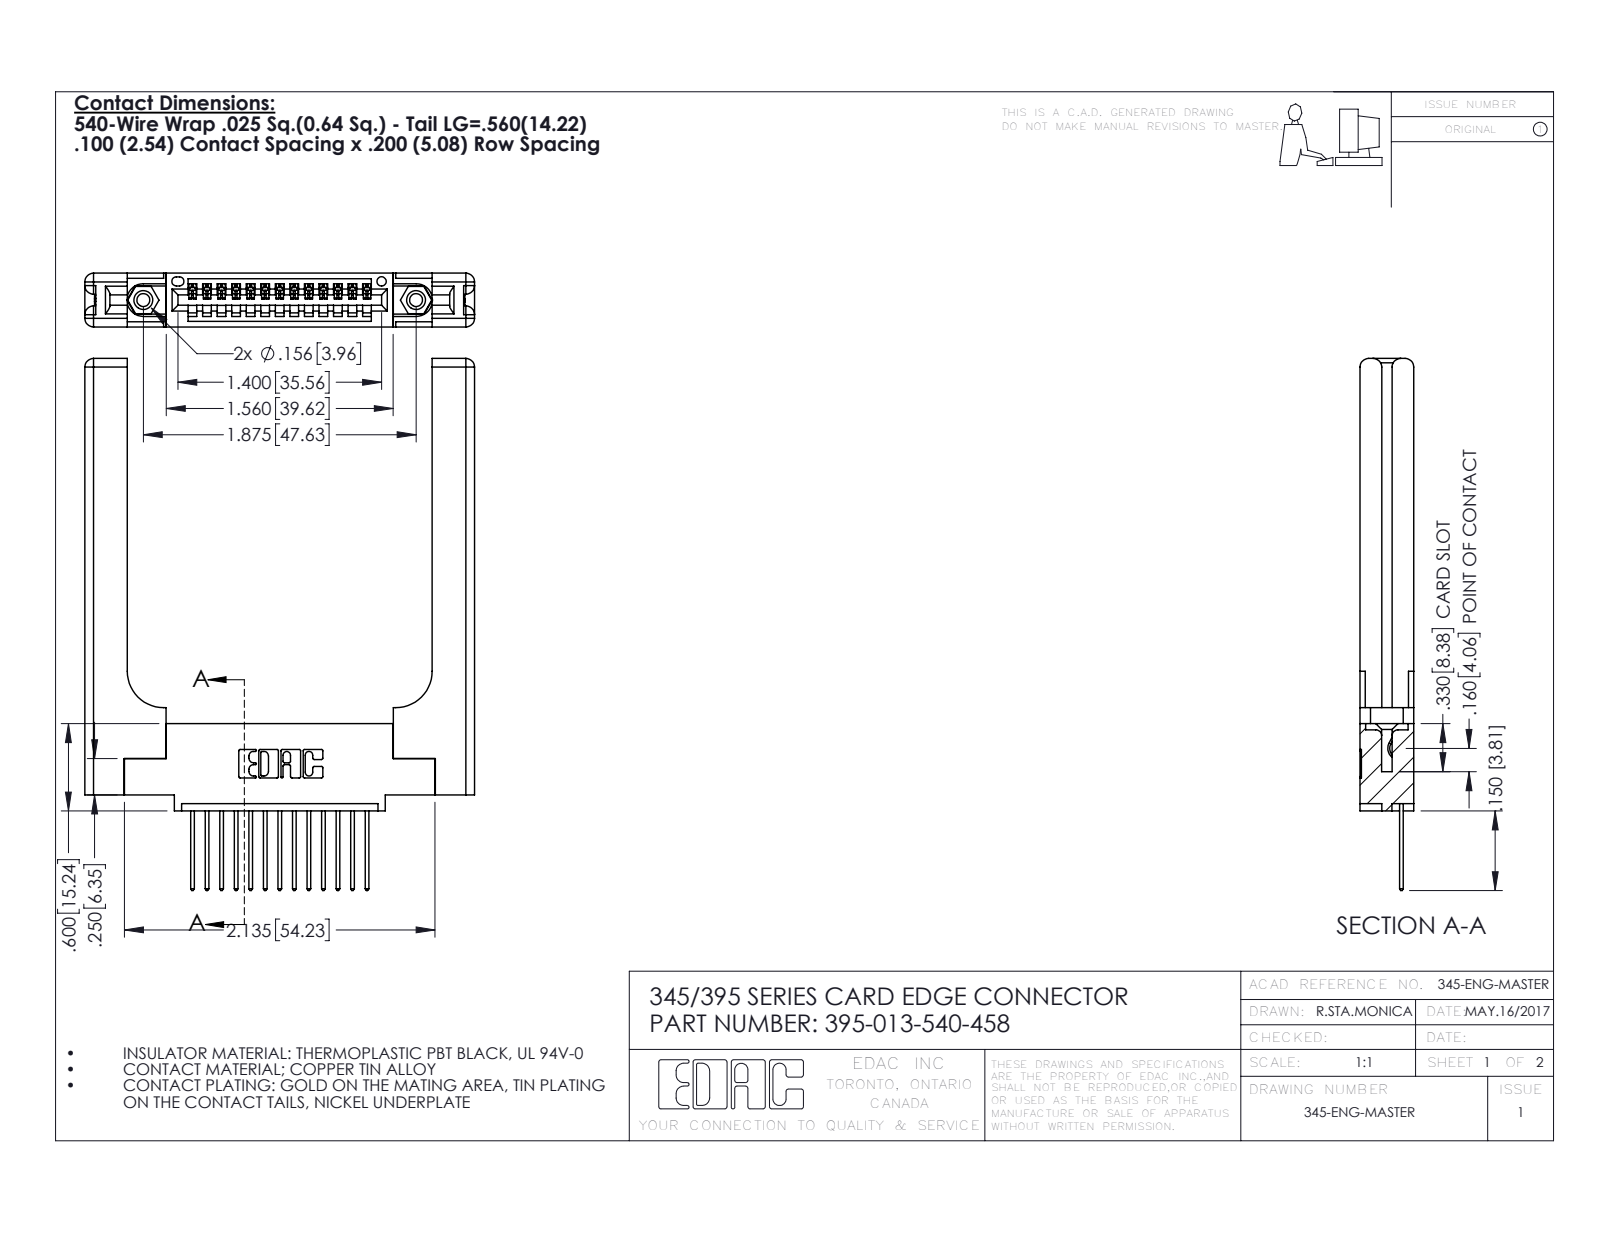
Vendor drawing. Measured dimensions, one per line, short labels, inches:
name: 345-292-001_345-293-140; 345 Part_0.110 Offset - 0.156 Dia-TH; 395-013-540-458; 345-220-058_345-220-058 (+1 more)
written by: SolidWorks 2016 (CONFIG_CONTROL_DESIGN)
unit: in
bodies: 18 solids, 1140 faces (752 planar, 328 cylindrical, 60 other)
size: 3.657 × 2.679 × 0.37
volume: 0.896 in³; area: 20.64 in²
holes: 2× ⌀0.089, 2× ⌀0.125, 2× ⌀0.156, 1× ⌀0.064
bosses: 2× ⌀0.155
rounds: 26× R0.006, 26× R0.01, 22× R0.01, 16× R0.06, 6× R0.007, 6× R0.031, 3× R0.026, 2× R0.03
face distances: 0.37, 0.072, 0.298, 0.15, 0.148, 0.077, 0.22, 0.098, 0.272, 0.025
hole spacings: 0.27, 1.643, 1.875
